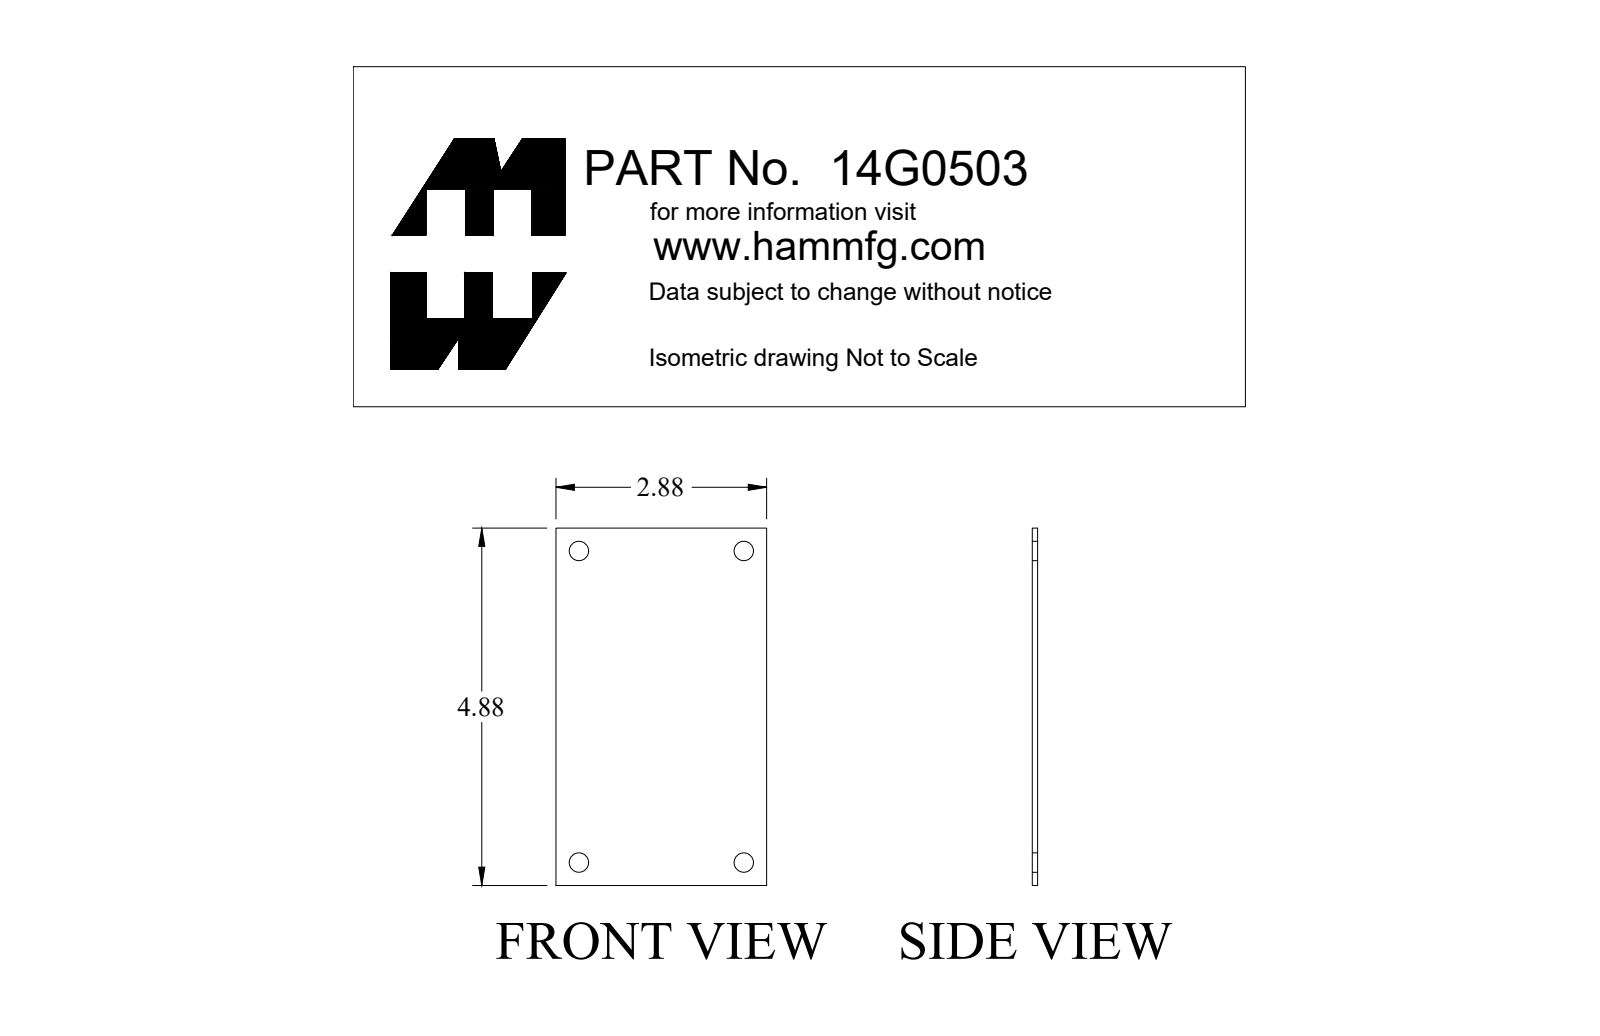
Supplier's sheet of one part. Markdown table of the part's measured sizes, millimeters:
| quantity | value |
| --- | --- |
| part name | 14G0503 |
| STEP written by | SolidWorks 2018 (AUTOMOTIVE_DESIGN) |
| units | millimeters |
| bodies | 1 solid, 10 faces (6 planar, 4 cylindrical, 0 other) |
| overall size | 123.8 × 73 × 1.8 |
| volume | 16 300 mm³ |
| surface area | 18 680 mm² |
| round holes (diameter × count) | 6.7 × 4 |
| main face-to-face distances | 1.8, 73, 123.8 |
| hole center spacings | 57.2, 108, 122.1 |
